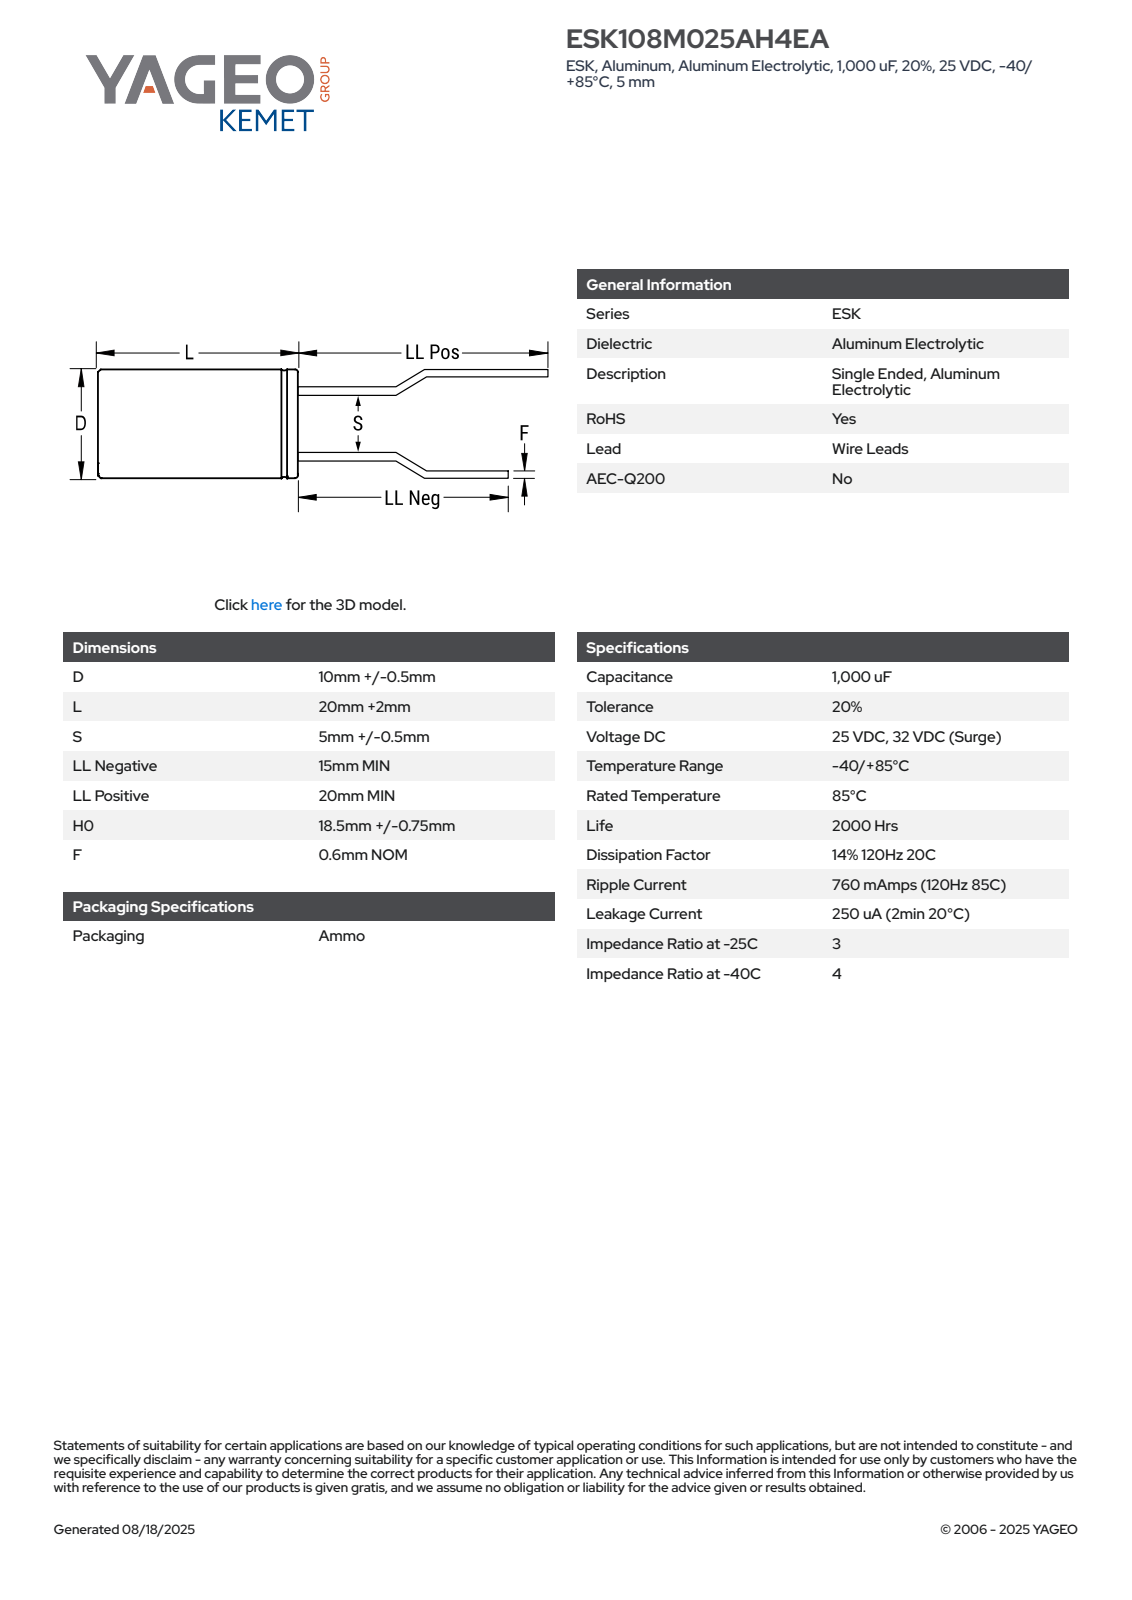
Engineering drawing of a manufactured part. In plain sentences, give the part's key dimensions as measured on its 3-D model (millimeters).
The part is named "CAR_KTRS_10X20_D10.5L22S5F0.6". Its 3-D file was written by "SolidWorks 2014 (AUTOMOTIVE_DESIGN)". It is 4 solids with 73 faces: 61 planar, 8 cylindrical and 4 other. Overall it measures 42.01 by 10.5 by 10.5 millimeters. Its volume is 1 903 cubic millimeters and its surface area 990 square millimeters. Round bosses or shafts: 2 of diameter 0.6, 1 of diameter 10.5. The main face-to-face distances are 22, 22.01, 37.01, 42.01, 37, 42, 15, 20, 5, 1.24.
